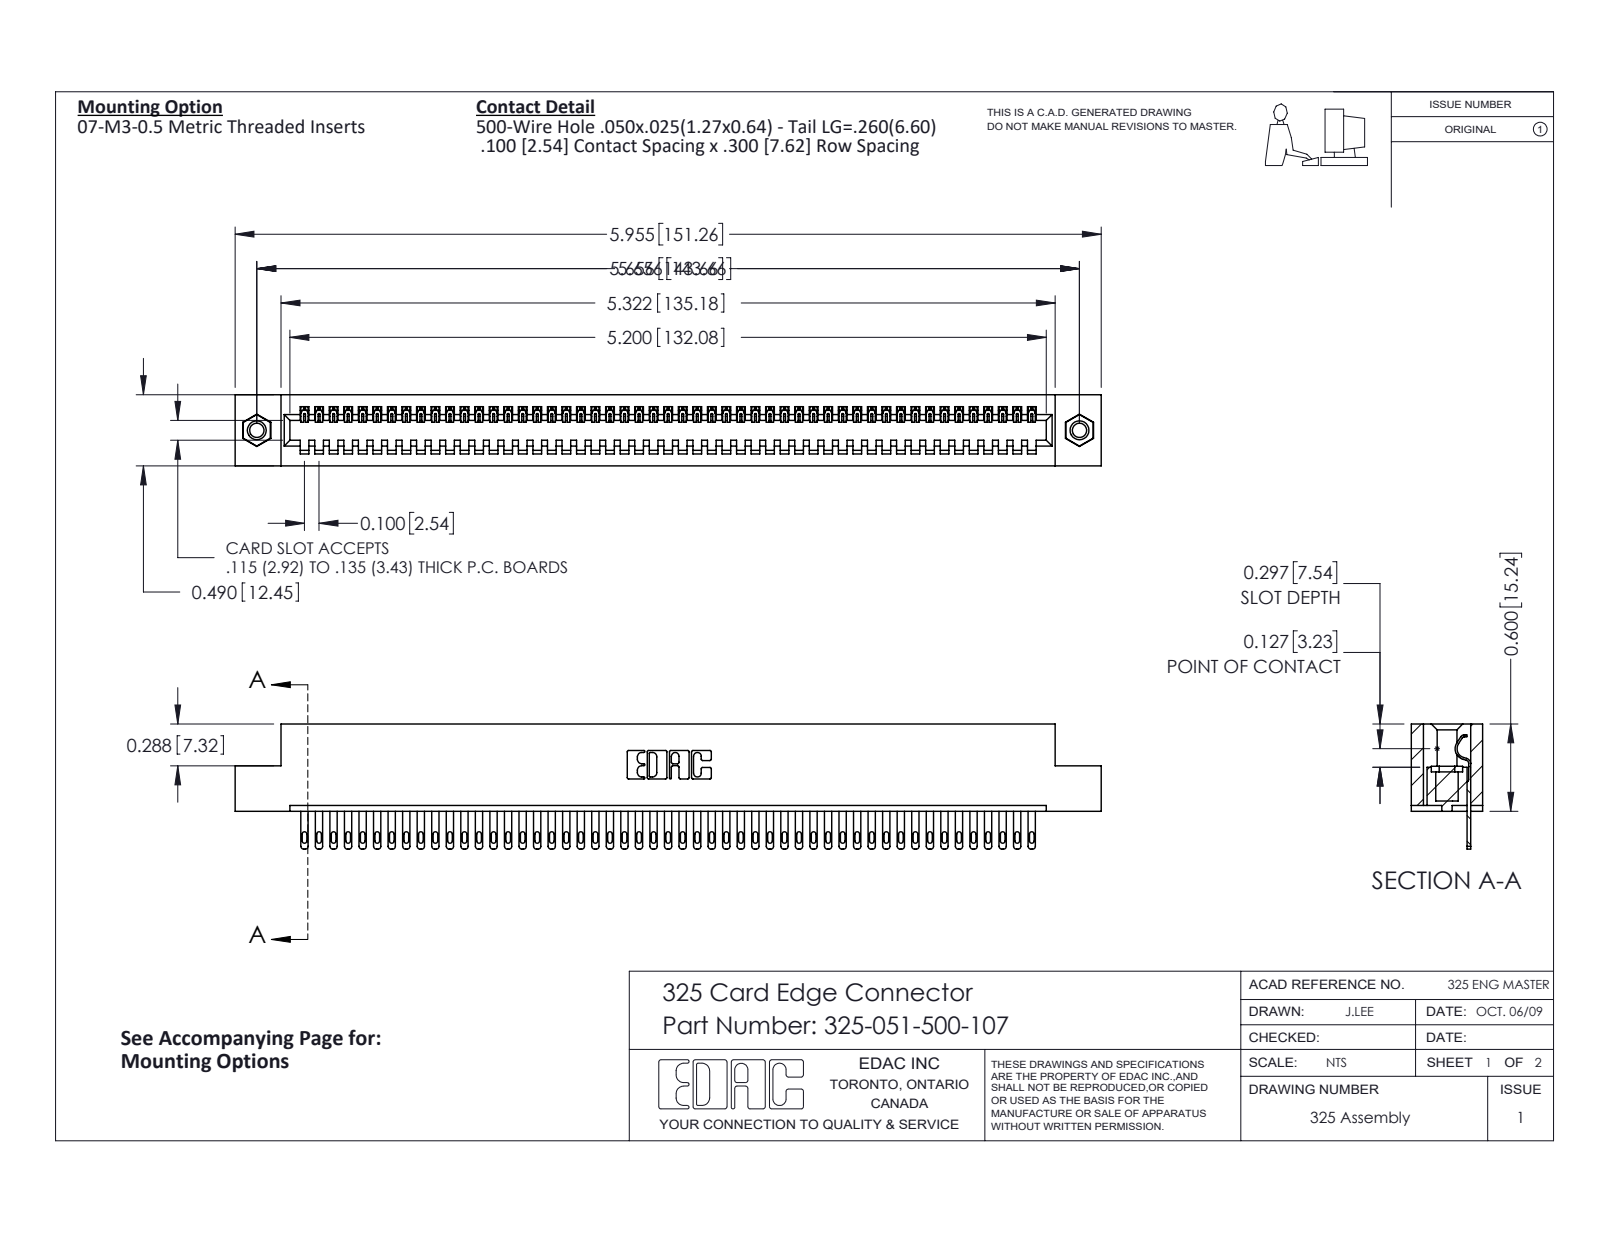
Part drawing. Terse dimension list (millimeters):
name: 325-292-001_325-293-100; 345-250-001_345-250-005-103; 325 Part_TI; 325-051-500-107
written by: SolidWorks 2016 (CONFIG_CONTROL_DESIGN)
unit: mm
bodies: 54 solids, 2928 faces (1938 planar, 974 cylindrical, 16 other)
size: 151.3 × 21.8 × 12.4
volume: 19 290 mm³; area: 21 370 mm²
holes: 2× ⌀2.5, 2× ⌀3.2, 2× ⌀4.1
bosses: 2× ⌀3.9
rounds: 102× R0.2, 102× R0.4, 102× R0.5, 22× R0.3, 6× R0.2, 6× R0.8, 3× R0.7, 1× R0.4
face distances: 2.1, 10.3, 12.4, 7.6, 2.7, 9.7, 0.6, 8.3, 14.2, 6.7
hole spacings: 143.7
